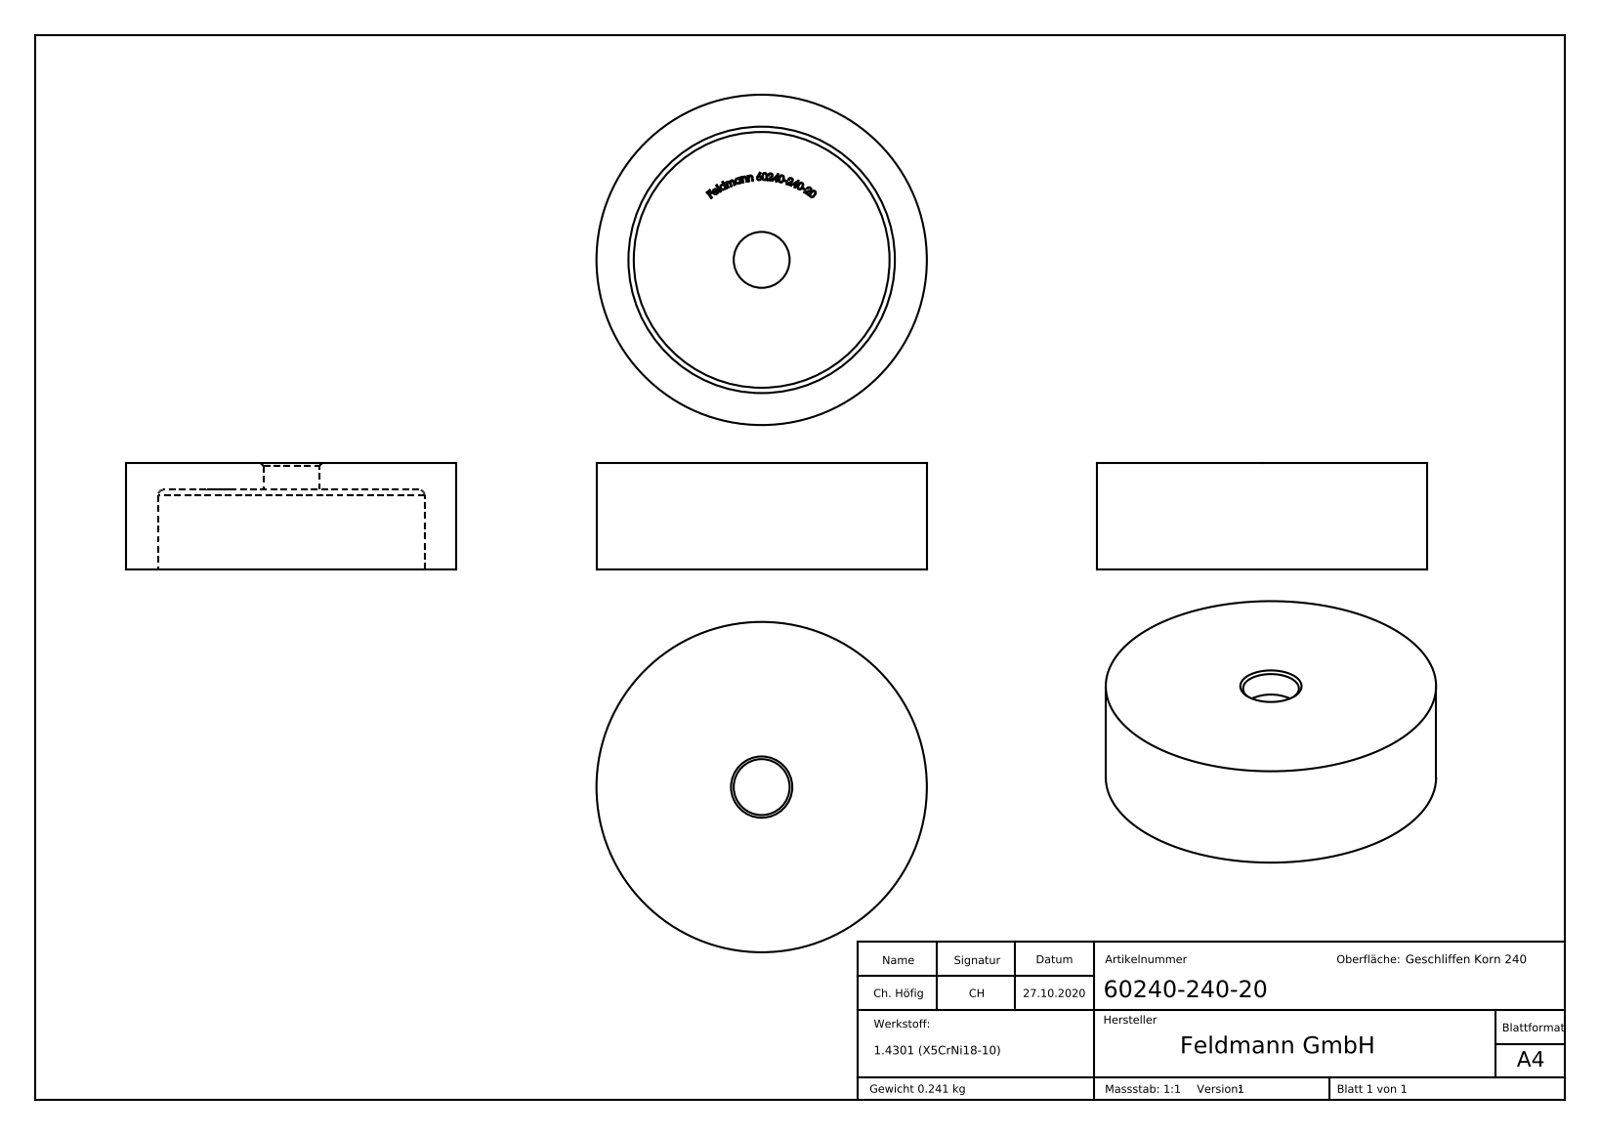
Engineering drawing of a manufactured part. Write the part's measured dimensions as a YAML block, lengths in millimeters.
part_name: "60240-240-20"
step_written_by: "SolidWorks 2018 (CONFIG_CONTROL_DESIGN)"
units: millimeters
bodies: {solids: 1, faces: 263, planar: 142, cylindrical: 6, other: 115}
overall_size: [62, 62, 20]
volume: 30525
surface_area: 12216
round_holes:
  - {diameter: 10.5, count: 1}
  - {diameter: 50, count: 1}
round_bosses_or_shafts:
  - {diameter: 62, count: 1}
face_to_face_distances: [5, 15, 20, 15.1, 4.9, 0.54, 1.33, 0.73, 1.46, 0.67]
